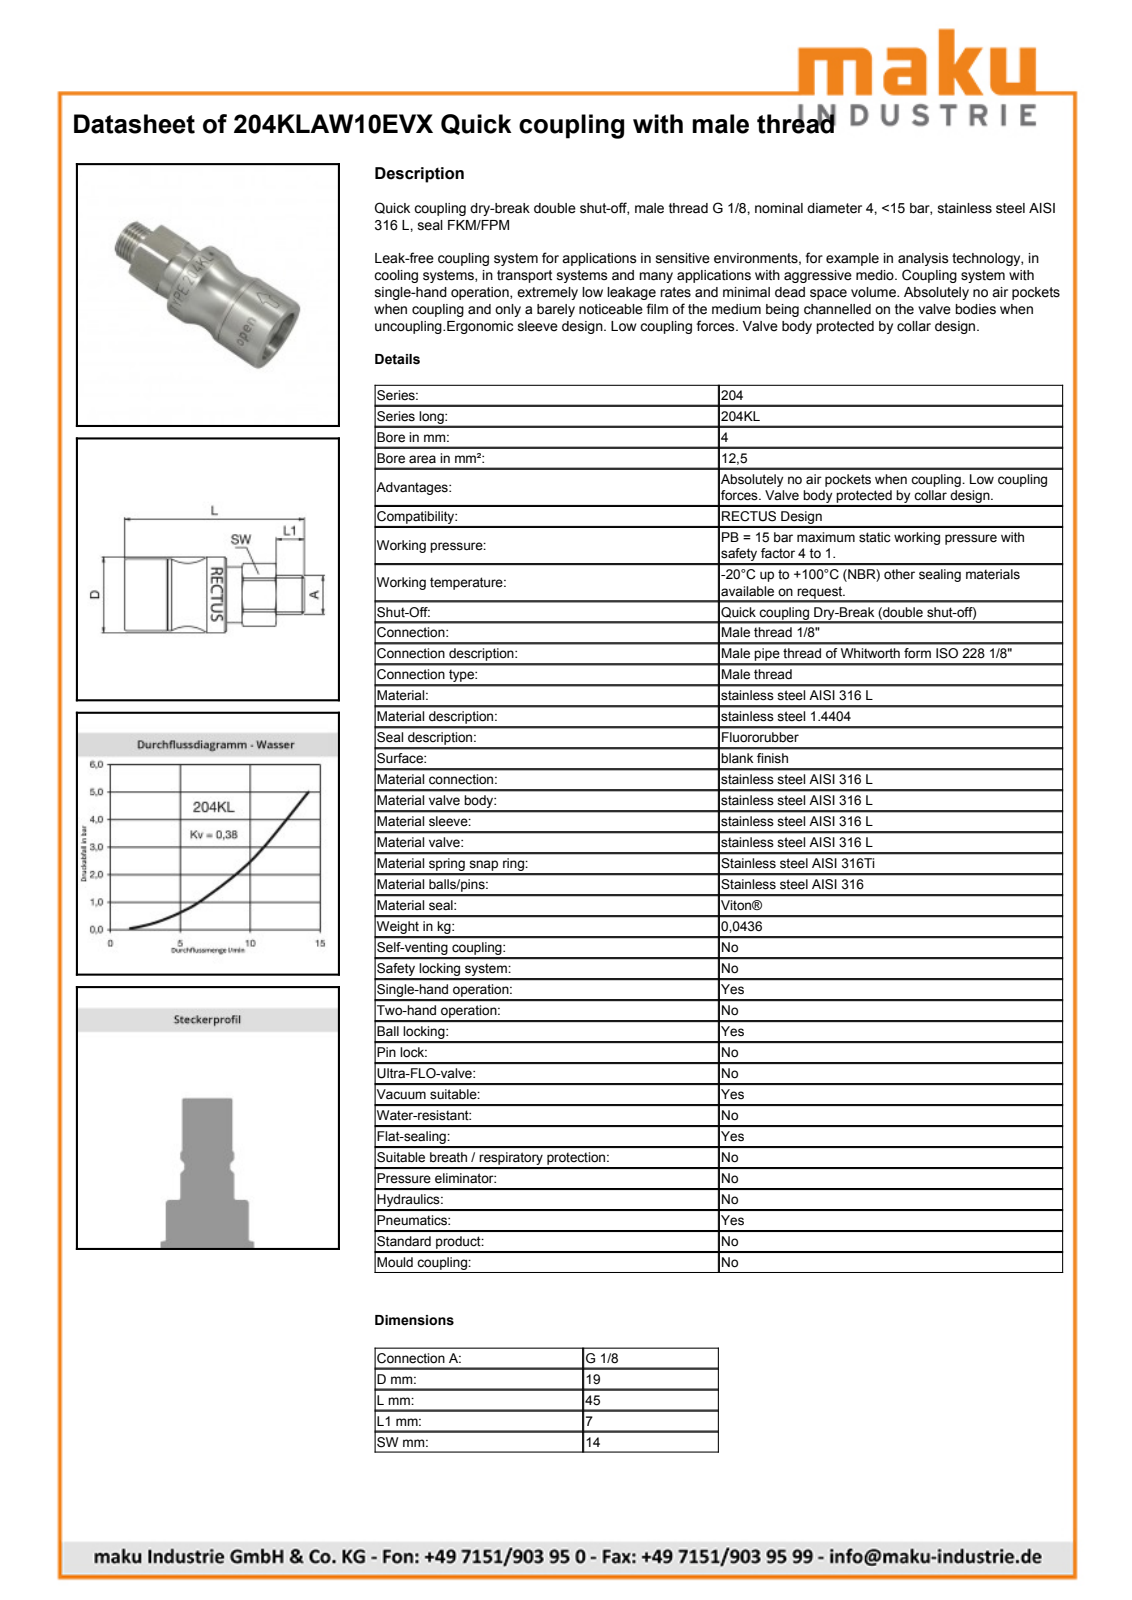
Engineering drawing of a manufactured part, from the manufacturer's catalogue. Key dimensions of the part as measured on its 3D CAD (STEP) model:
Part name (STEP PRODUCT): D111033
STEP written by: Autodesk Inventor 2013 (AUTOMOTIVE_DESIGN)
Units: millimetres
Bodies: 2 solids, 813 faces (337 planar, 113 cylindrical, 363 other)
Overall size (bounding box): 44.9 × 19 × 19
Volume: 7 216 mm³ · Surface area: 5 958 mm²
Round holes (diameter × count): ⌀11 ×1, ⌀12 ×1, ⌀12.6 ×1, ⌀12.7 ×1, ⌀14.05 ×1, ⌀14.2 ×1, ⌀14.6 ×1, ⌀17 ×1, ⌀17.2 ×1
Round bosses / shafts (diameter × count): ⌀19 ×1, ⌀18 ×1, ⌀16.35 ×1, ⌀14.8 ×1, ⌀14 ×1, ⌀13 ×1, ⌀12.5 ×1, ⌀11.3 ×1
Partial cylindrical surfaces — rounded edges, fillets, slot ends (radius × count): R7.9 ×1, R8.9 ×1, R9.4 ×1
Main face-to-face distances: 14, 2, 2.5, 23.05, 1.25, 25.55, 23.55, 37.9, 35.9, 12.35
